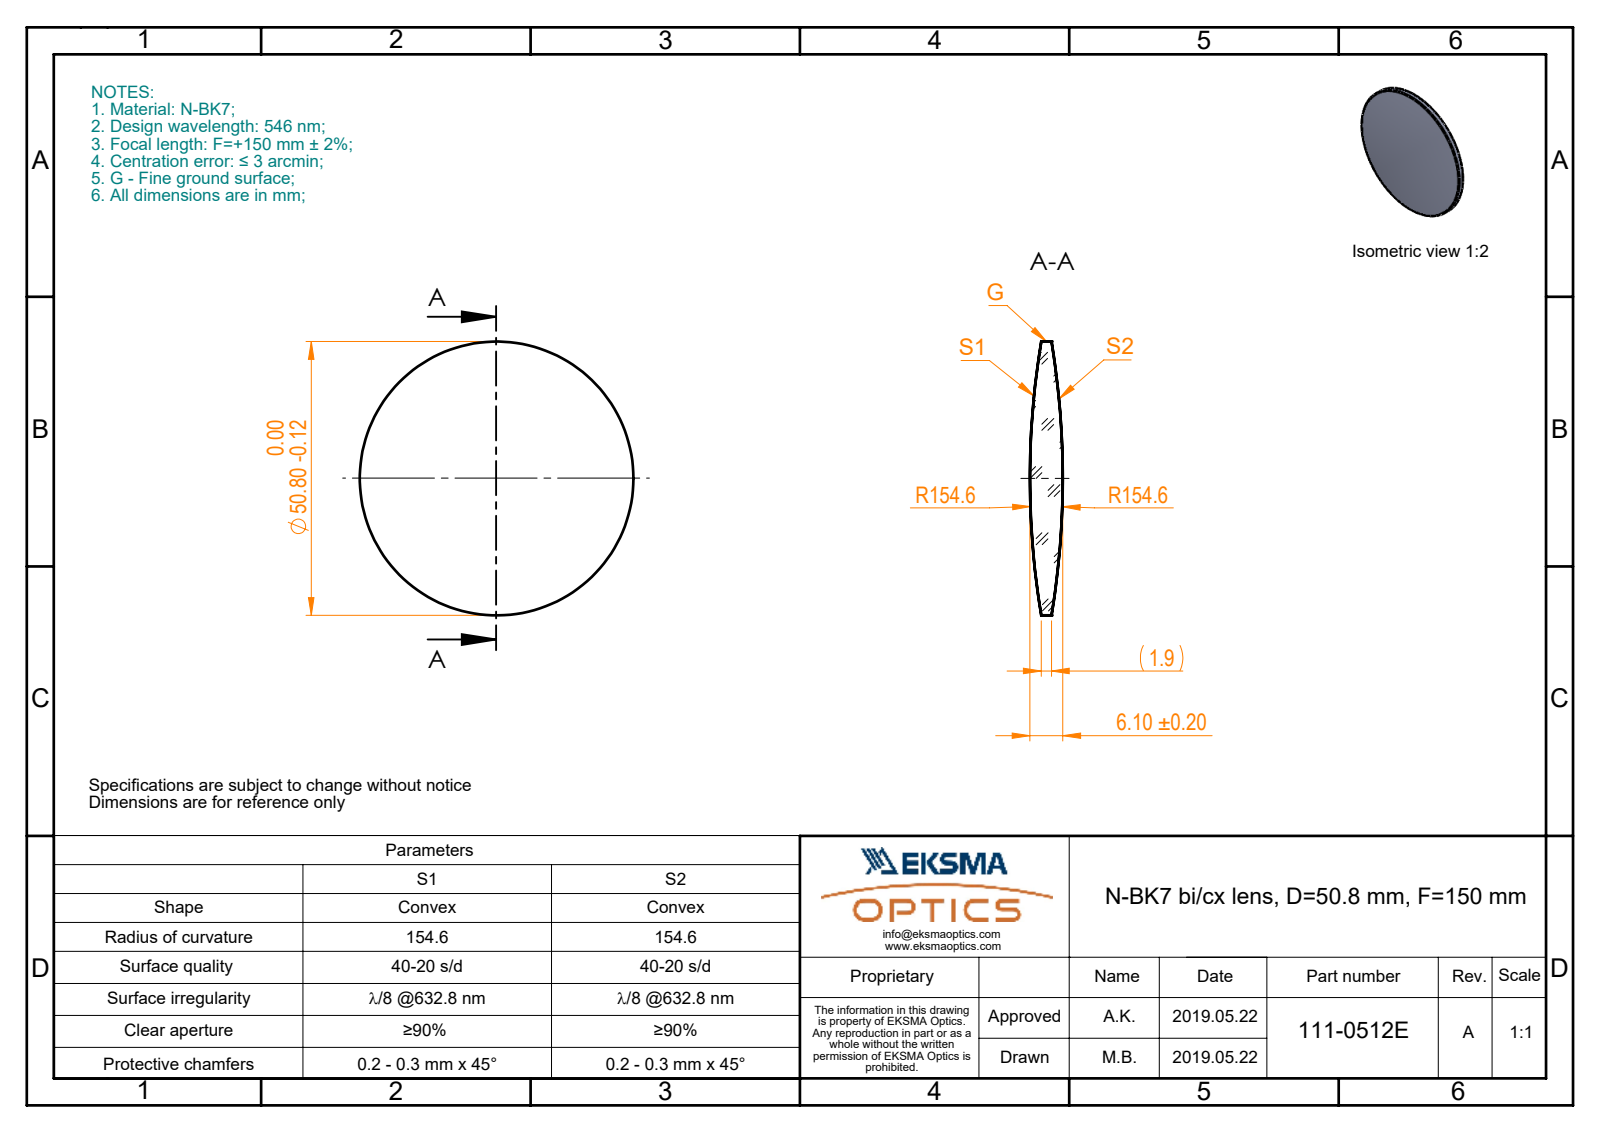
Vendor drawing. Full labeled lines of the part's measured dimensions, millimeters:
Part name (STEP PRODUCT): 111-0512E BK7 bi-cx 50.8 F150
STEP written by: SolidWorks 2017 (CONFIG_CONTROL_DESIGN)
Units: millimetres
Bodies: 1 solid, 6 faces (0 planar, 2 cylindrical, 4 other)
Overall size (bounding box): 50.8 × 50.8 × 6.1
Volume: 8 115 mm³ · Surface area: 4 384 mm²
Round bosses / shafts (diameter × count): ⌀50.8 ×1
